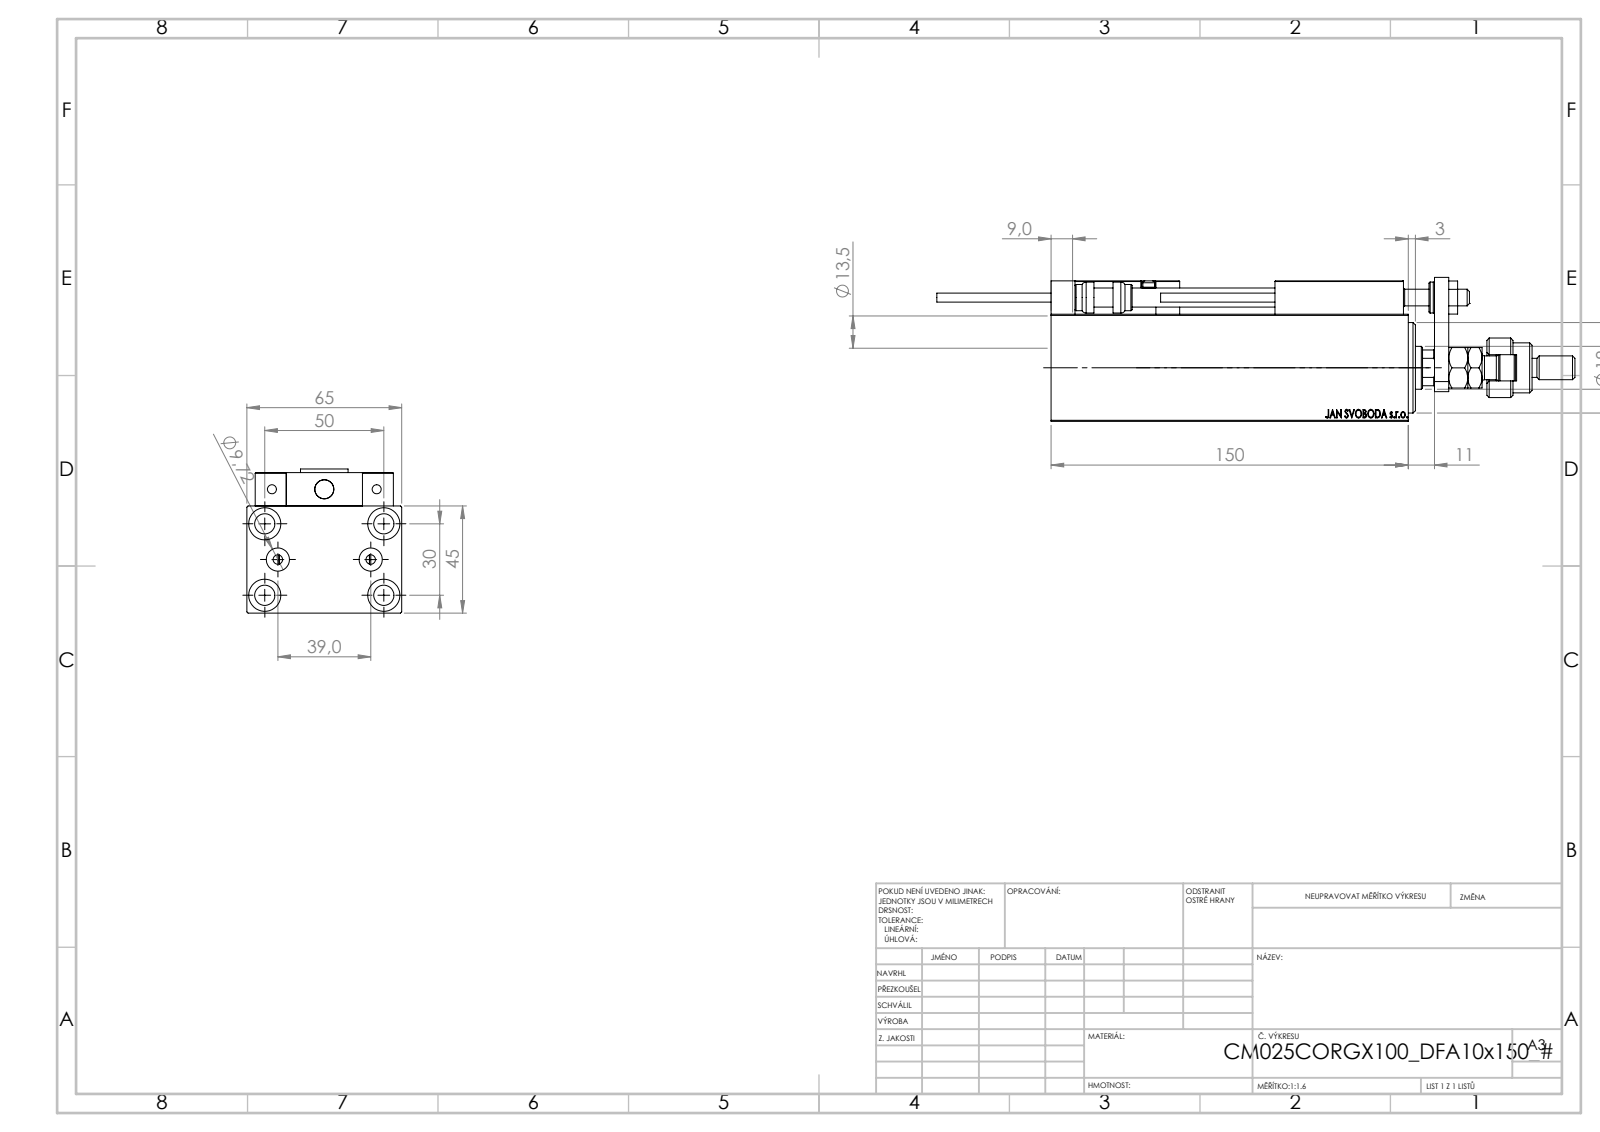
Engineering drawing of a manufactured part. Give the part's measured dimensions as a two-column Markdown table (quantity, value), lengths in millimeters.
| quantity | value |
| --- | --- |
| part name | MAGNET; Block; KONCOVKA; V450CM_VC_B (+7 more) |
| STEP written by | SolidWorks 2019 (CONFIG_CONTROL_DESIGN) |
| units | millimeters |
| bodies | 25 solids, 1363 faces (588 planar, 197 cylindrical, 578 other) |
| overall size | 268 × 65 × 60.5 |
| volume | 434 688 mm³ |
| surface area | 116 285 mm² |
| round holes (diameter × count) | 4 × 6, 8 × 5, 8.5 × 5, 3.2 × 4, 13.5 × 4, 5 × 2, 9.72 × 2, 7 × 1, 14.5 × 1, 18 × 1, 21.5 × 1, 27 × 1 |
| round bosses / shafts (diameter × count) | 5 × 2, 3.8 × 2, 25 × 1, 21 × 1, 16 × 1, 13 × 1, 11 × 1, 10 × 1 |
| partial cylindrical surfaces (radius × count) | 0.3 × 30, 3 × 2, 5.5 × 1, 8.5 × 1, 8.75 × 1 |
| main face-to-face distances | 45, 65, 14, 6, 59, 3, 7, 161, 19, 13 |
| hole center spacings | 15.98, 29.15, 46.96, 11.37, 19.5, 20, 28.9, 29.59 |
